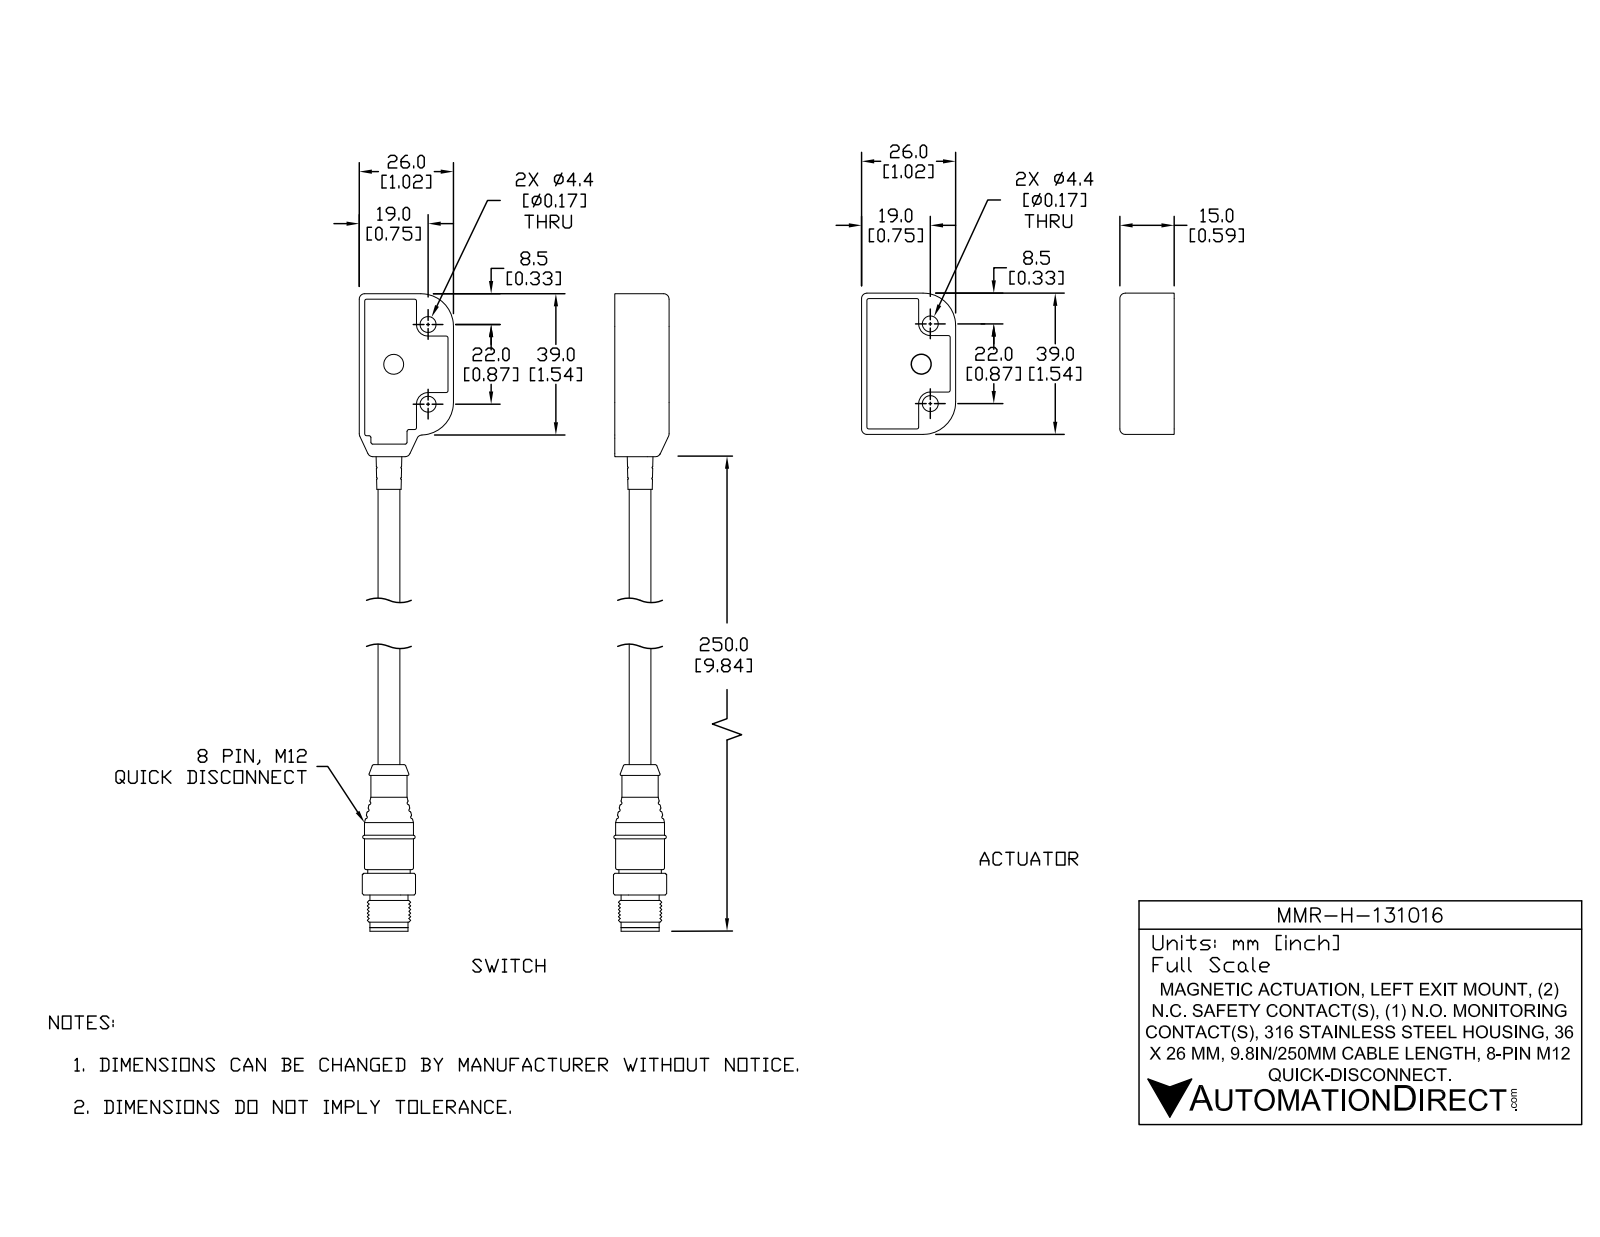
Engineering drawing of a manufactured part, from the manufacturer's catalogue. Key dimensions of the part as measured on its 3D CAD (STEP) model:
Part name (STEP PRODUCT): MMR-H-131016; MMR-H-131016_1; MMR-H-131016_2
STEP written by: SolidWorks 2017 (AUTOMOTIVE_DESIGN)
Units: inches
Bodies: 10 solids, 963 faces (335 planar, 348 cylindrical, 280 other)
Overall size (bounding box): 11.713 × 2.087 × 0.604
Volume: 1.615 in³ · Surface area: 38.4 in²
Round holes (diameter × count): ⌀0.173 ×4, ⌀0.197 ×2, ⌀0.118 ×1, ⌀0.232 ×1, ⌀0.283 ×1, ⌀0.327 ×1, ⌀0.394 ×1, ⌀0.465 ×1
Round bosses / shafts (diameter × count): ⌀0.031 ×10, ⌀0.079 ×2, ⌀0.531 ×1, ⌀0.461 ×1, ⌀0.413 ×1, ⌀0.374 ×1, ⌀0.339 ×1, ⌀0.299 ×1
Partial cylindrical surfaces — rounded edges, fillets, slot ends (radius × count): R0.02 ×83, R0.012 ×26, R0.059 ×15, R0.008 ×8, R0.157 ×6, R0.126 ×4, R0.13 ×4, R0.181 ×4
Main face-to-face distances: 0.059, 0.575, 0.516, 0.098, 0.461, 0.52, 0.055, 0.591, 0.531, 0.965
Hole centre spacings: 0.572, 0.866, 1.239, 1.535, 1.763, 0.076, 0.44, 0.448
